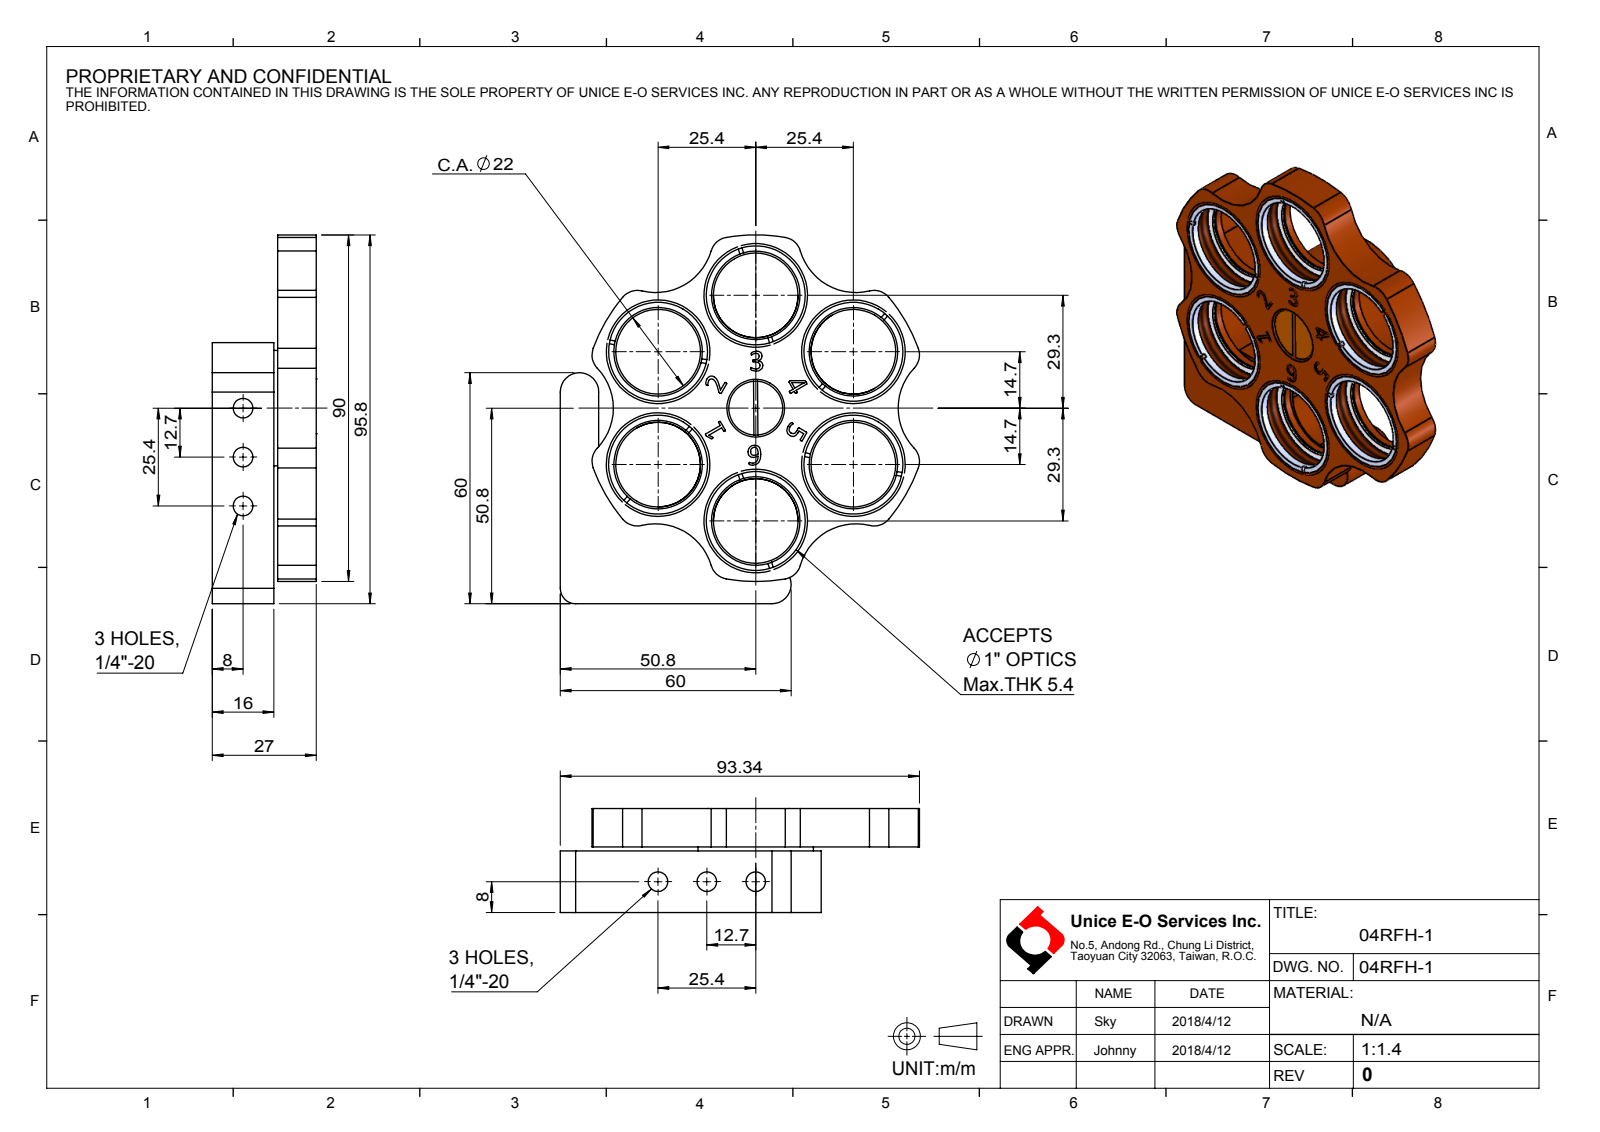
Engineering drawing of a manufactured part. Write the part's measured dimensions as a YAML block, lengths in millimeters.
part_name: "04RFH-1"
step_written_by: "SolidWorks 2016 (CONFIG_CONTROL_DESIGN)"
units: millimeters
bodies: {solids: 21, faces: 408, planar: 114, cylindrical: 191, other: 103}
overall_size: [95.8, 93.34, 27]
volume: 69744
surface_area: 37749
round_holes:
  - {diameter: 1.5, count: 12}
  - {diameter: 22, count: 8}
  - {diameter: 5.11, count: 6}
  - {diameter: 19.5, count: 6}
  - {diameter: 26.3, count: 6}
  - {diameter: 5, count: 4}
  - {diameter: 7, count: 1}
  - {diameter: 10, count: 1}
  - {diameter: 15, count: 1}
round_bosses_or_shafts:
  - {diameter: 25, count: 6}
  - {diameter: 26.3, count: 4}
  - {diameter: 6, count: 3}
  - {diameter: 30, count: 1}
  - {diameter: 14, count: 1}
  - {diameter: 5, count: 1}
partial_cylinders:
  - {radius: 5, count: 14}
  - {radius: 15, count: 6}
  - {radius: 10, count: 2}
  - {radius: 20, count: 2}
  - {radius: 4, count: 1}
  - {radius: 11, count: 1}
  - {radius: 17, count: 1}
  - {radius: 45, count: 1}
face_to_face_distances: [1, 3, 4.6, 10, 16, 5.6, 17, 11, 27, 4]
hole_center_spacings: [29.3, 36.08, 11, 51.93, 25.63, 41.59, 50.75, 60.53]
